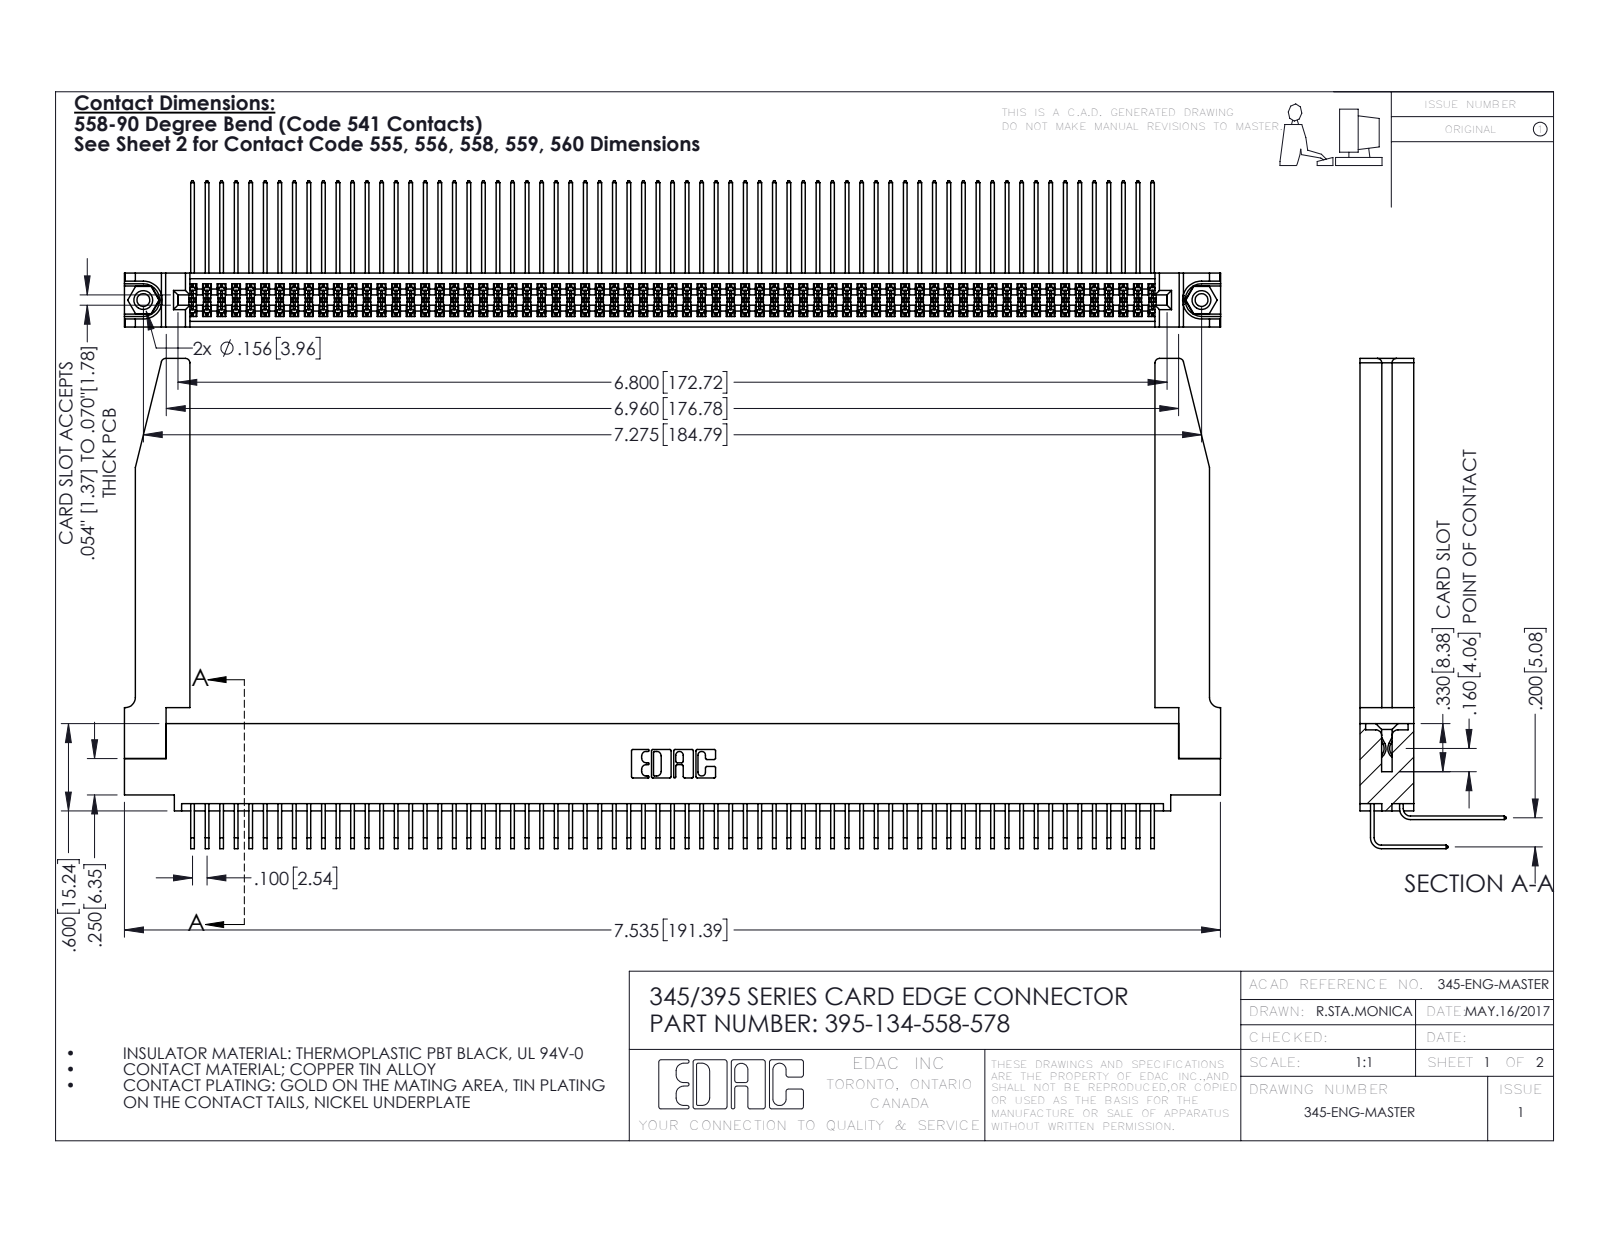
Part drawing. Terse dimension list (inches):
name: 345 Part_0.110 Offset - 0.156 Dia-TH; 345-292-001_558 559 Tail - 1; 345-250-001_345-250-001-102; 345-292-001_558 Tail - 2 (+2 more)
written by: SolidWorks 2016 (CONFIG_CONTROL_DESIGN)
unit: in
bodies: 139 solids, 7332 faces (4916 planar, 2364 cylindrical, 52 other)
size: 7.536 × 3.369 × 1.005
volume: 1.666 in³; area: 61.87 in²
holes: 2× ⌀0.089, 2× ⌀0.125, 2× ⌀0.156, 1× ⌀0.064
bosses: 2× ⌀0.155
rounds: 202× R0.006, 22× R0.01, 8× R0.03, 6× R0.007, 6× R0.031, 3× R0.026, 2× R0.014, 2× R0.019
face distances: 0.072, 0.298, 0.37, 0.2, 0.098, 0.272, 0.025, 0.225, 0.025, 0.175
hole spacings: 0.27, 7.039, 7.275
